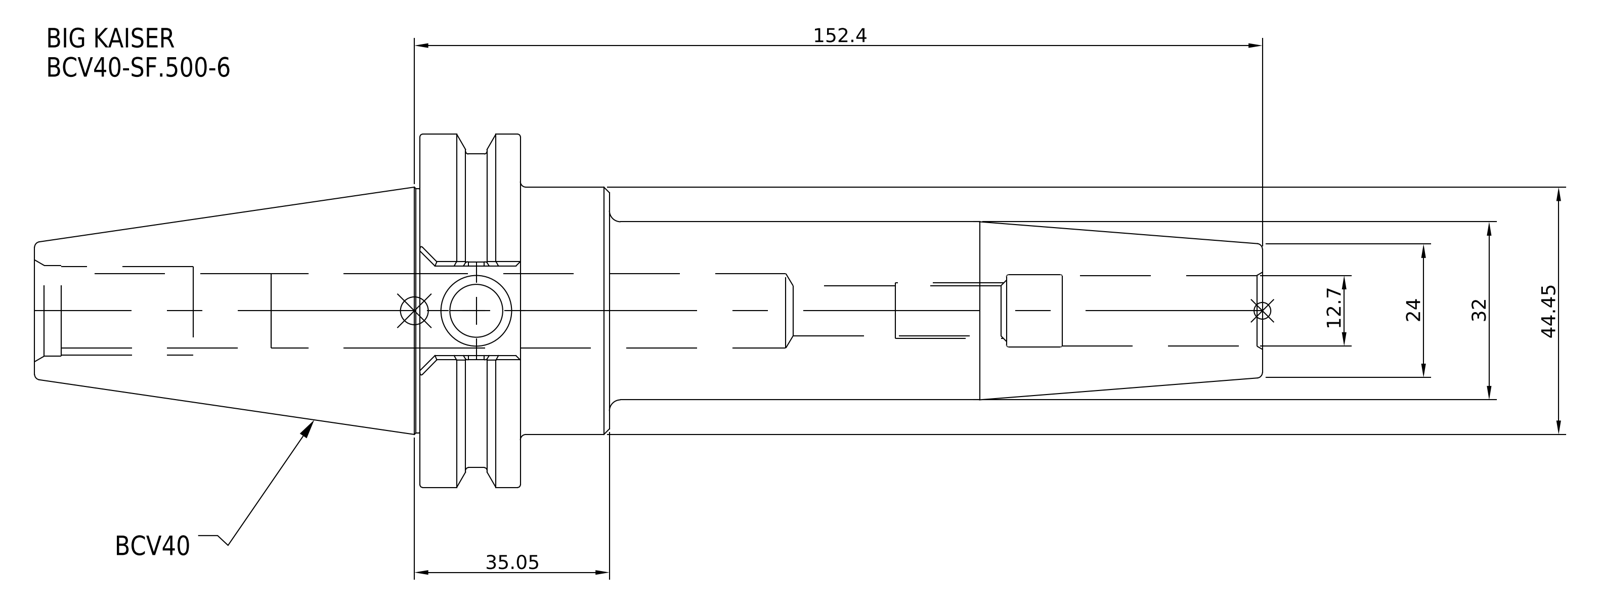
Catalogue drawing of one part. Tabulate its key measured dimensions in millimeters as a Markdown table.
| quantity | value |
| --- | --- |
| part name | BCV40-SF_500-6 |
| STEP written by | SolidWorks 2021 (CONFIG_CONTROL_DESIGN) |
| units | millimeters |
| bodies | 1 solid, 30 faces (8 planar, 14 cylindrical, 8 other) |
| overall size | 220.65 × 63.5 × 63.5 |
| volume | 226 108 mm³ |
| surface area | 31 745 mm² |
| round holes (diameter × count) | 12.7 × 1 |
| round bosses / shafts (diameter × count) | 63.5 × 1, 56.36 × 1, 44.45 × 1, 32 × 1 |
| main face-to-face distances | 18.05, 16, 34.05, 103.3, 87.3, 69.25, 117.35, 133.35, 151.4, 220.65 |
